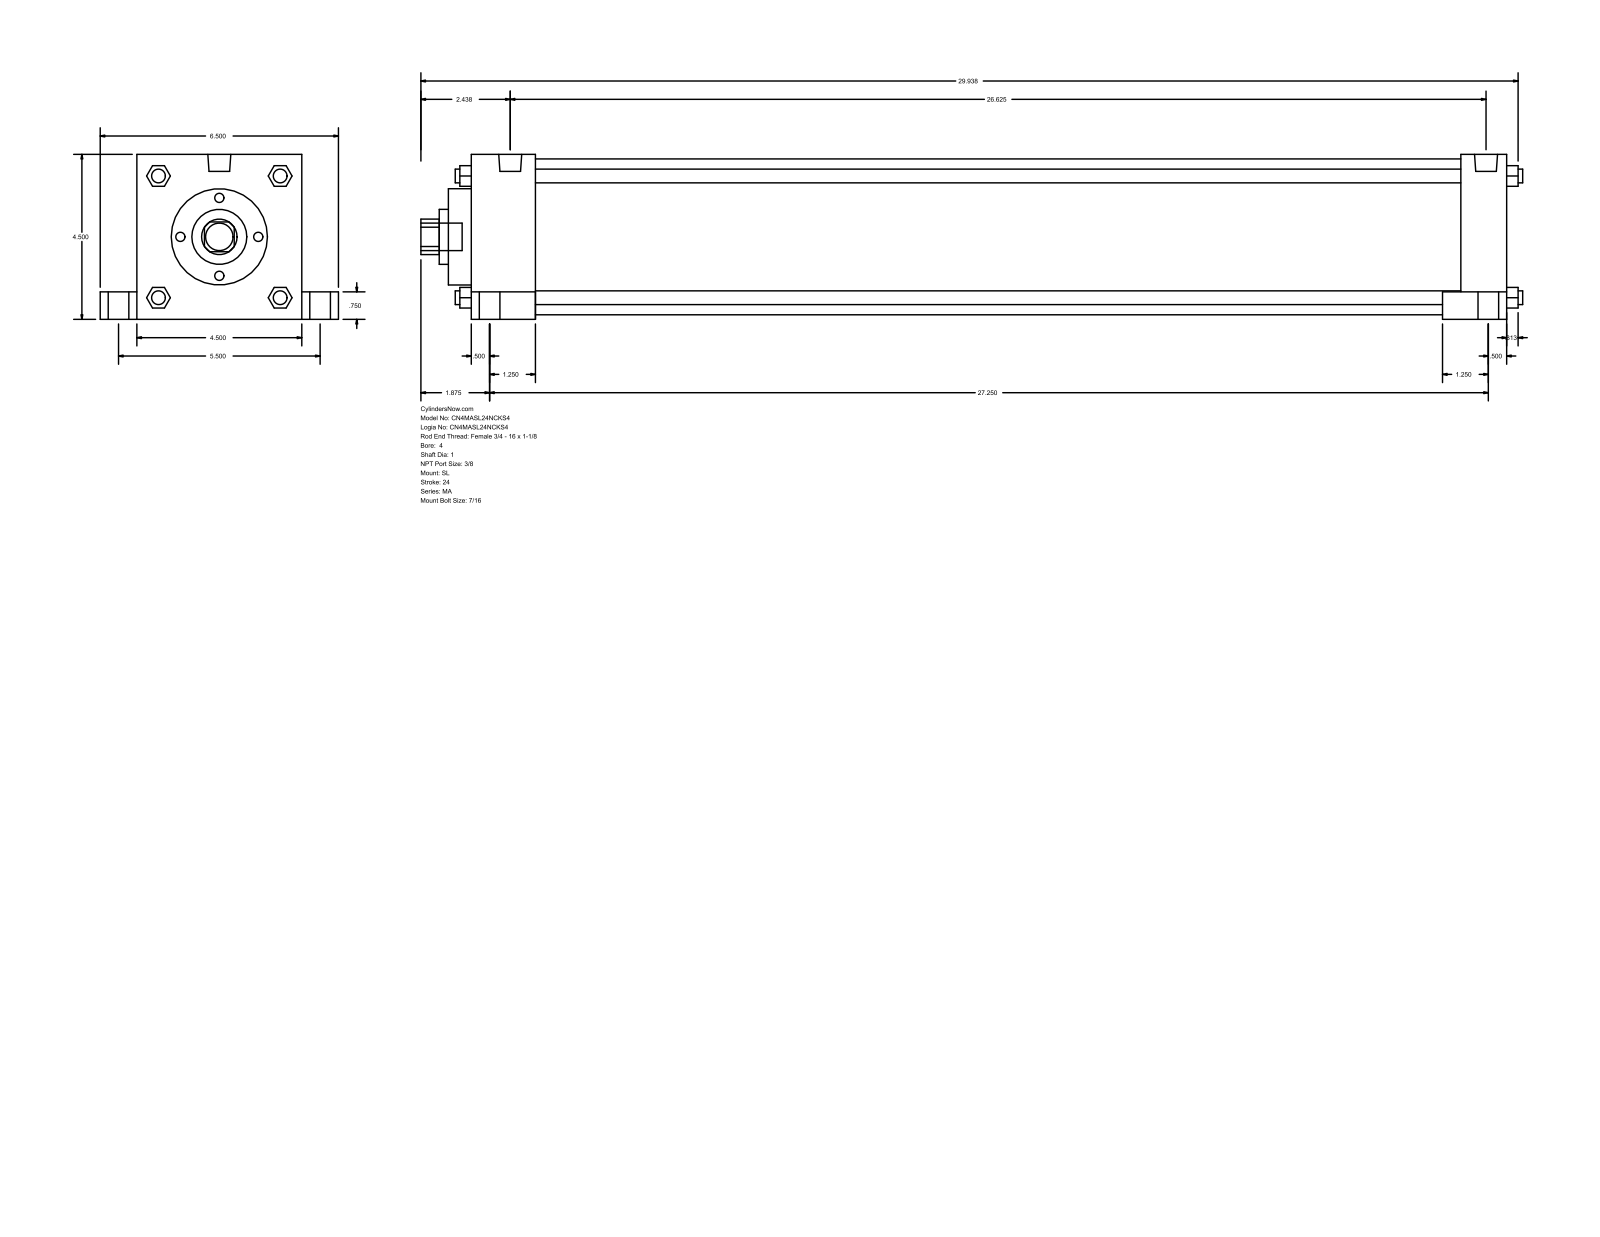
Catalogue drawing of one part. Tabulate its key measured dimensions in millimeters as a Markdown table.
| quantity | value |
| --- | --- |
| part name | MA_SL__0400_1 |
| STEP written by | GSSL Pune (CONFIG_CONTROL_DESIGN) |
| units | millimeters |
| bodies | 0 solids, 150 faces (113 planar, 37 cylindrical, 0 other) |
| overall size | 763.59 × 165.1 × 114.3 |
| round holes (diameter × count) | 25.4 × 1, 38.1 × 1, 66.67 × 1, 107.95 × 1 |
| round bosses / shafts (diameter × count) | 20.64 × 4, 14.29 × 4, 11.11 × 4, 9.53 × 4, 15.93 × 2, 19.05 × 1 |
| partial cylindrical surfaces (radius × count) | 12.29 × 1 |
| main face-to-face distances | 114.3, 717.56, 641.35, 44.46, 673.1, 685.81, 31.75, 25.4, 139.7, 19.05 |
